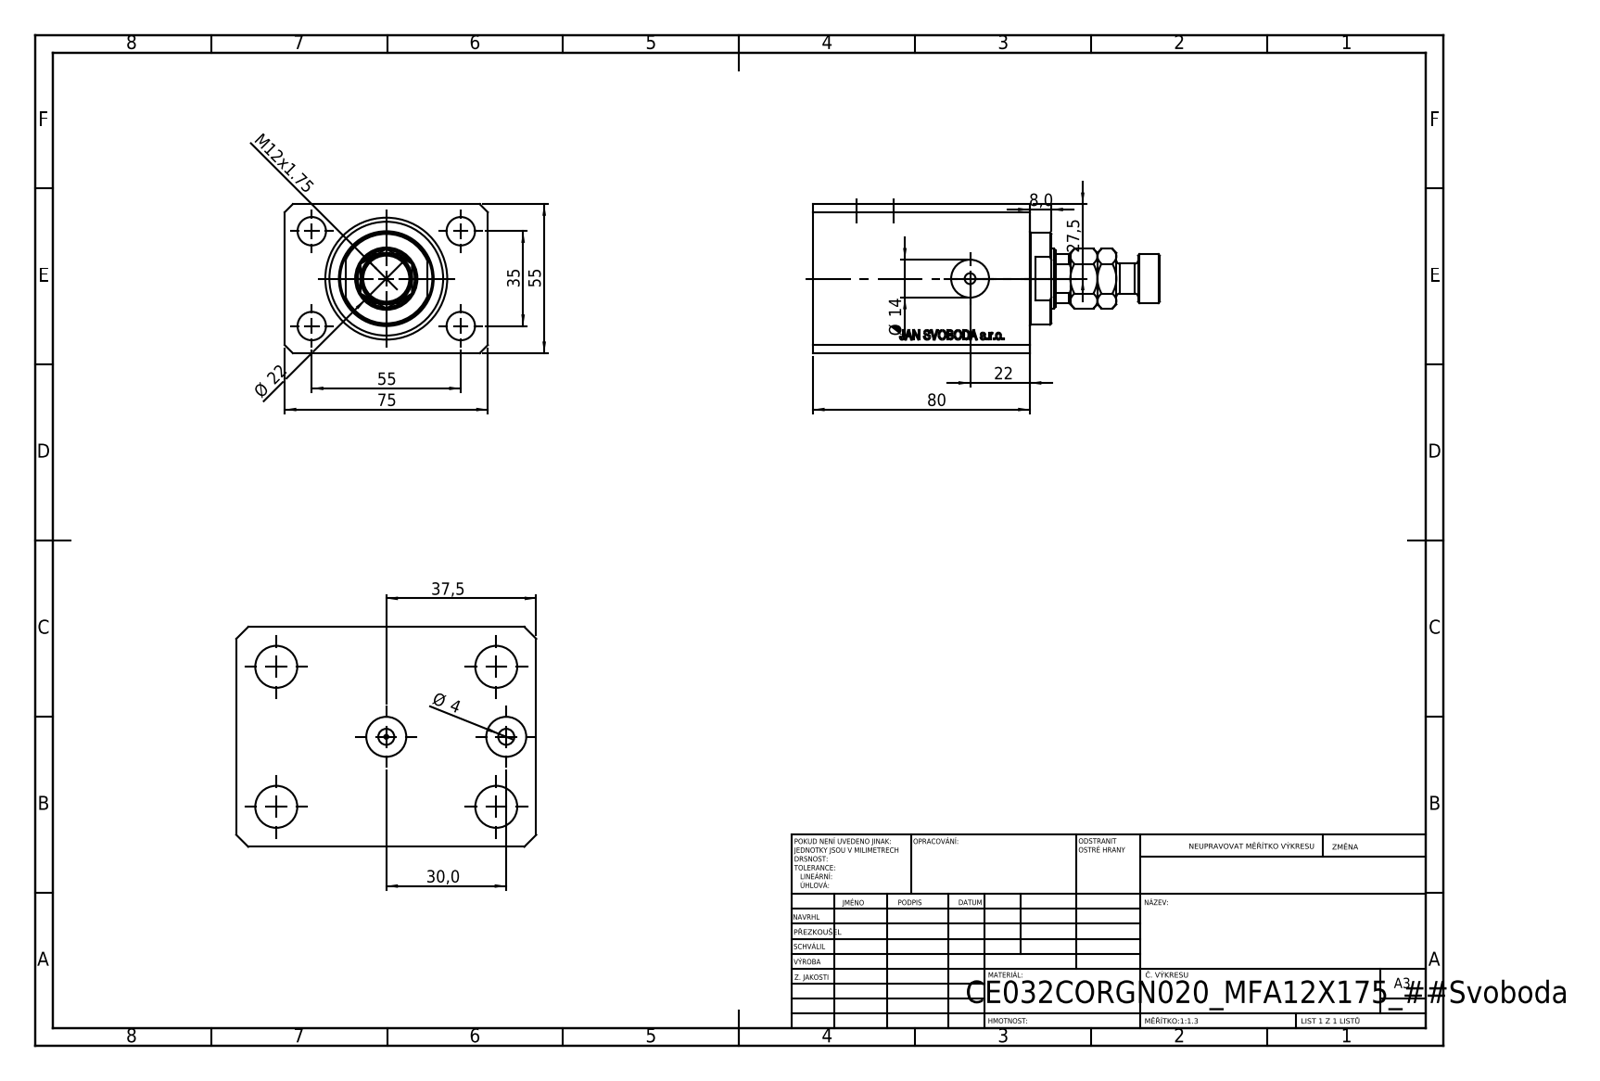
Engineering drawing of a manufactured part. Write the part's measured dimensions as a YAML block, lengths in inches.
part_name: "V250CE_C_Body; V250CE_C_VCP; V250CE_VC_C; MFA"
step_written_by: "SolidWorks 2019 (CONFIG_CONTROL_DESIGN)"
units: inches
bodies: {solids: 4, faces: 924, planar: 444, cylindrical: 54, other: 426}
overall_size: [5.039, 2.953, 2.165]
volume: 18.57
surface_area: 104.4
round_holes:
  - {diameter: 0.413, count: 5}
  - {diameter: 0.157, count: 4}
  - {diameter: 0.394, count: 2}
  - {diameter: 0.551, count: 2}
  - {diameter: 0.049, count: 1}
  - {diameter: 0.866, count: 1}
  - {diameter: 1.26, count: 1}
  - {diameter: 1.772, count: 1}
round_bosses_or_shafts:
  - {diameter: 1.339, count: 1}
  - {diameter: 0.709, count: 1}
  - {diameter: 0.433, count: 1}
partial_cylinders:
  - {radius: 0.413, count: 1}
face_to_face_distances: [2.165, 2.953, 3.15, 0.591, 2.559, 0.39, 2.169, 2.76, 0.315, 3.451]
hole_center_spacings: [1.283, 0.696, 1.378, 2.165, 2.366, 2.567, 1.181, 1.417]
